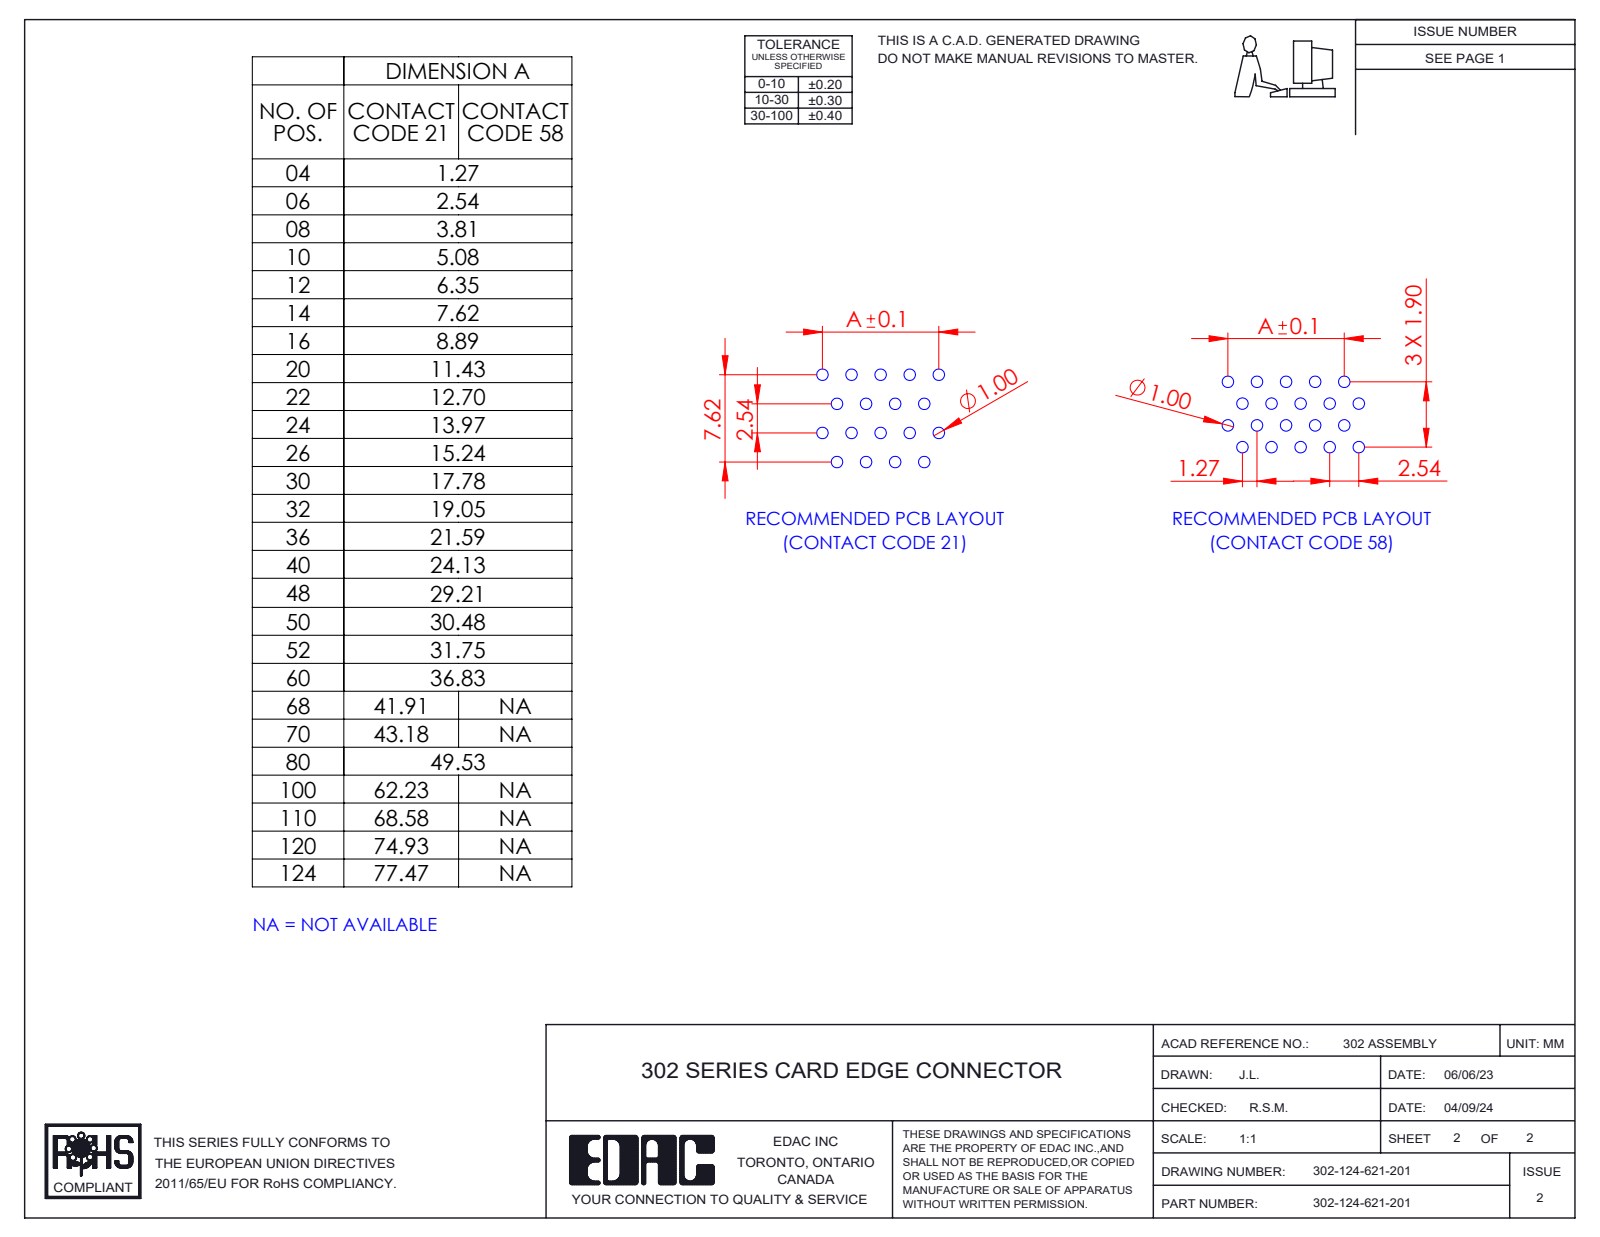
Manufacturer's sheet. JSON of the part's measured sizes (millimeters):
{"part_name": "302-124-621-201; HSG_Vertical HSG; Contact_302-290-X21 (2); Contact_302-290-X21 (1)", "step_written_by": "SolidWorks 2023 (CONFIG_CONTROL_DESIGN)", "units": "millimeters", "bodies": {"solids": 125, "faces": 5708, "planar": 4203, "cylindrical": 1253, "other": 252}, "overall_size": [84.84, 17.63, 8.88], "volume_mm3": 6440, "surface_area_mm2": 18527, "partial_cylinders_radius": [[0.2, 132], [2.03, 4], [2.09, 4], [0.11, 2], [0.4, 2], [0.41, 2], [1.25, 2], [1.53, 2]], "face_to_face_distances": [8.88, 2.54, 1.27, 5.08, 3.81, 0.8, 0.47, 3.49, 5.39, 1.9]}
